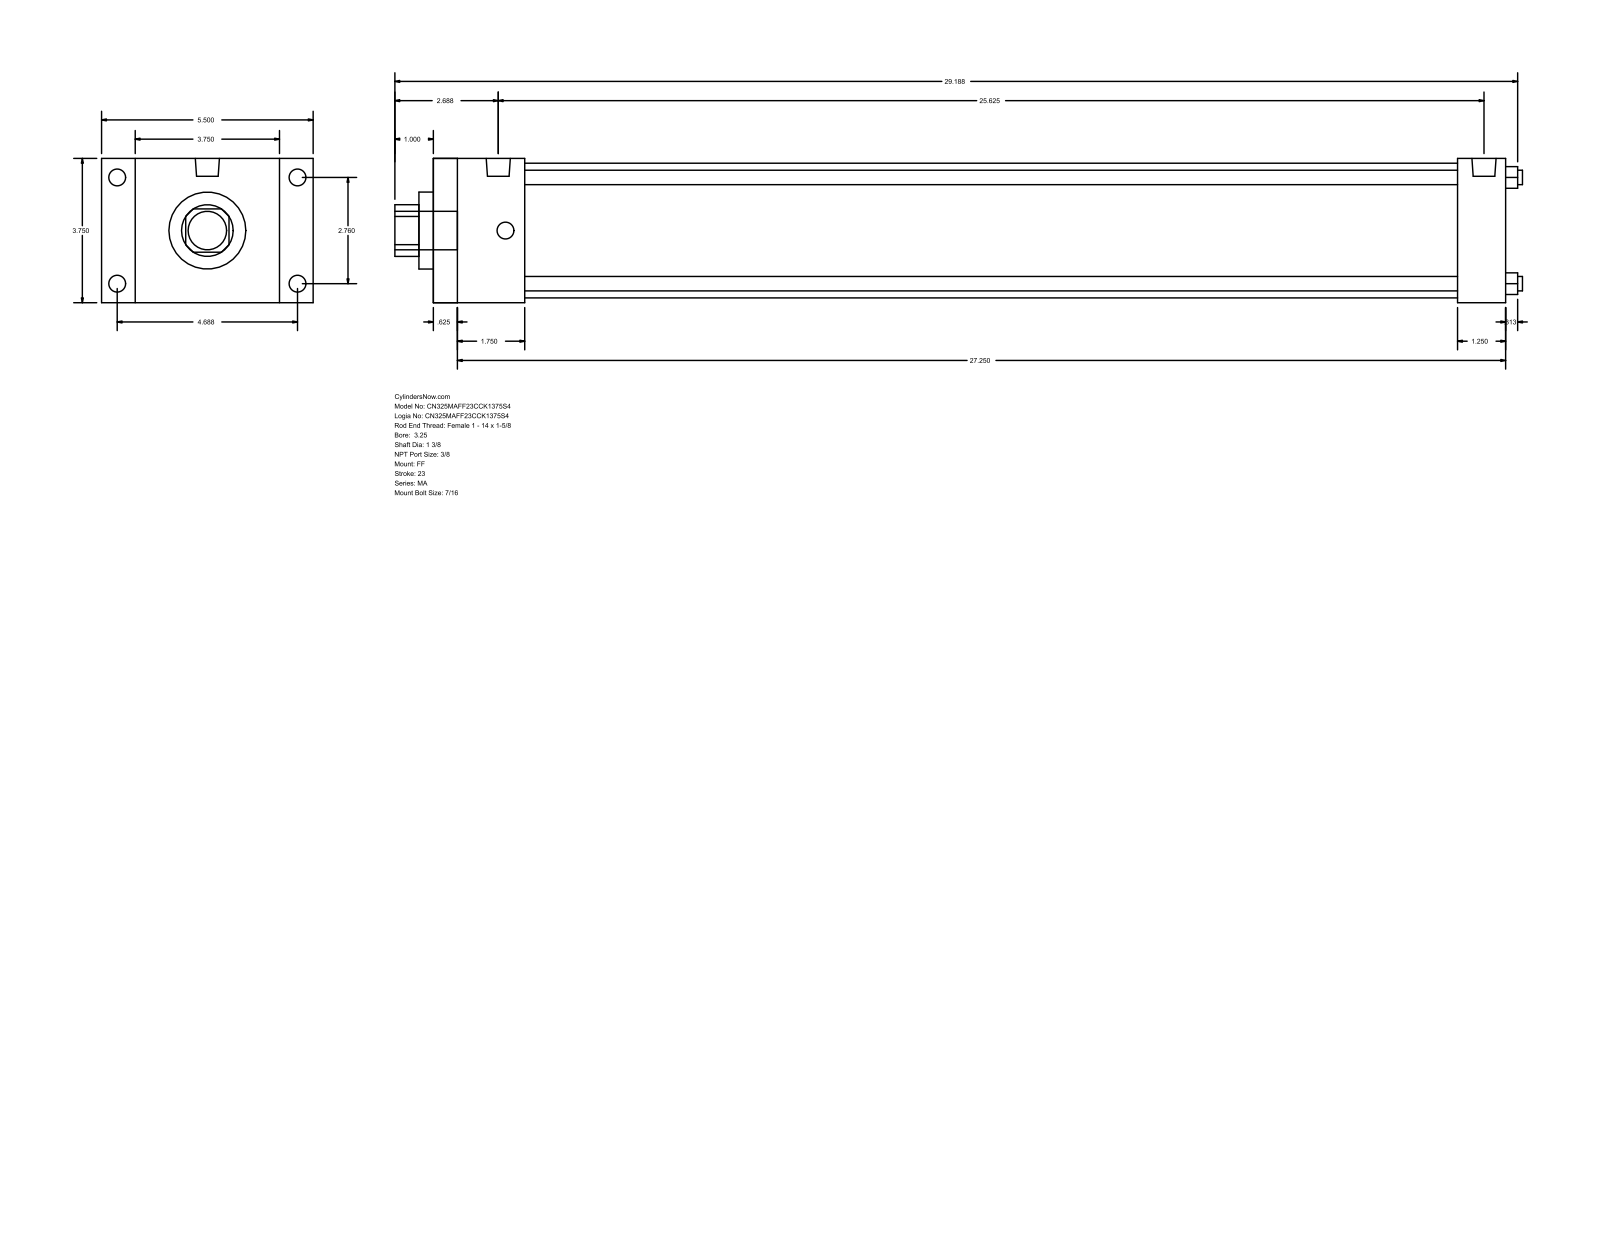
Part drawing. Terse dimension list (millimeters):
name: MA_FF__0325_1.375
written by: GSSL Pune (CONFIG_CONTROL_DESIGN)
unit: mm
bodies: 0 solids, 92 faces (64 planar, 28 cylindrical, 0 other)
size: 744.54 × 139.7 × 95.25
holes: 4× ⌀9.53, 1× ⌀34.92, 1× ⌀50.8, 1× ⌀88.9
bosses: 8× ⌀11.11, 2× ⌀15.93, 1× ⌀25.4
rounds: 1× R17.06
face distances: 95.24, 708.02, 15.87, 692.15, 22.23, 117.47, 60.32, 676.27, 44.45, 660.4
hole spacings: 49.57, 70.1, 99.14
